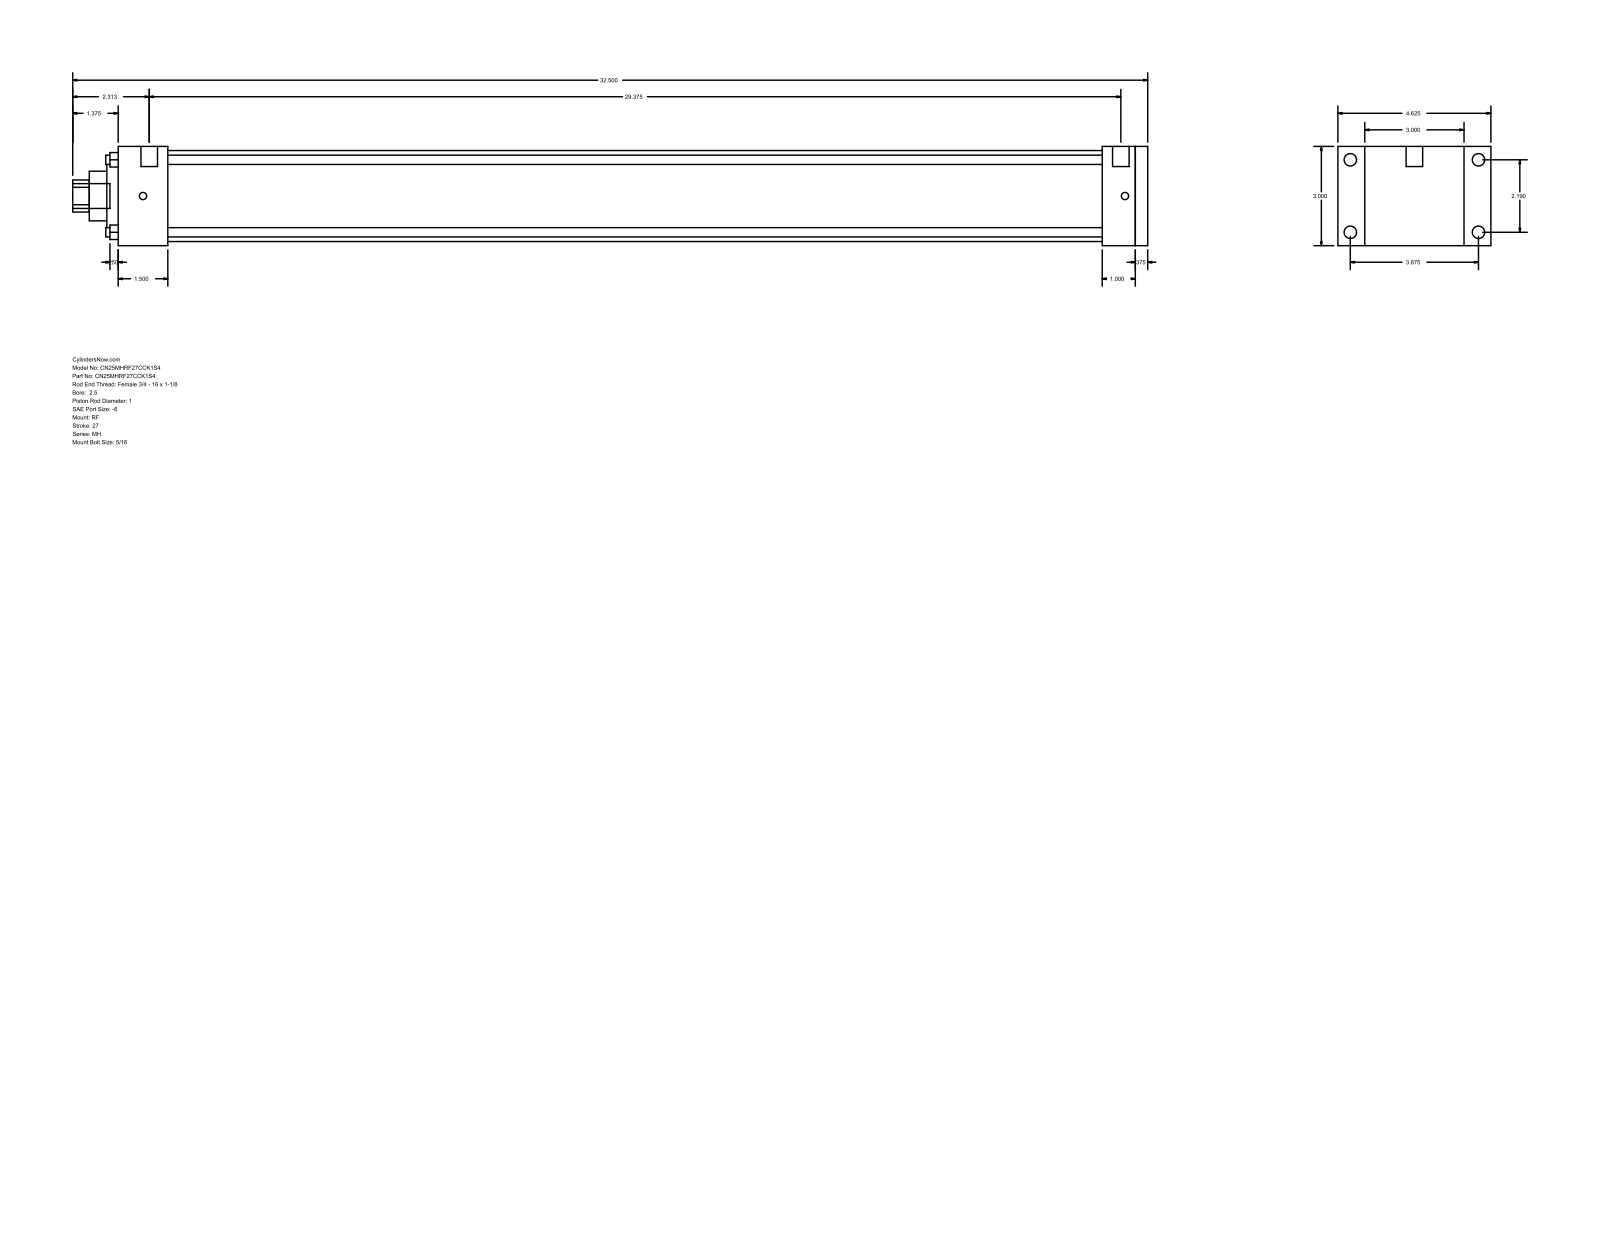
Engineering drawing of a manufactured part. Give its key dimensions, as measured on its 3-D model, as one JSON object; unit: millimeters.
{"part_name": "MH_RF__0250_1", "step_written_by": "GSSL Pune (CONFIG_CONTROL_DESIGN)", "units": "millimeters", "bodies": {"solids": 0, "faces": 94, "planar": 65, "cylindrical": 29, "other": 0}, "overall_size": [825.5, 117.47, 76.2], "round_holes": [[7.14, 4], [25.4, 1], [38.1, 1], [60.33, 1], [69.85, 1]], "round_bosses_or_shafts": [[9.53, 4], [5.56, 4], [12.7, 2], [19.05, 1]], "partial_cylinders_radius": [[12.29, 1]], "face_to_face_distances": [76.2, 9.52, 790.58, 781.06, 25.4, 34.92, 755.66, 38.11, 717.55, 742.95], "hole_center_spacings": [39.33, 55.62, 78.66]}
